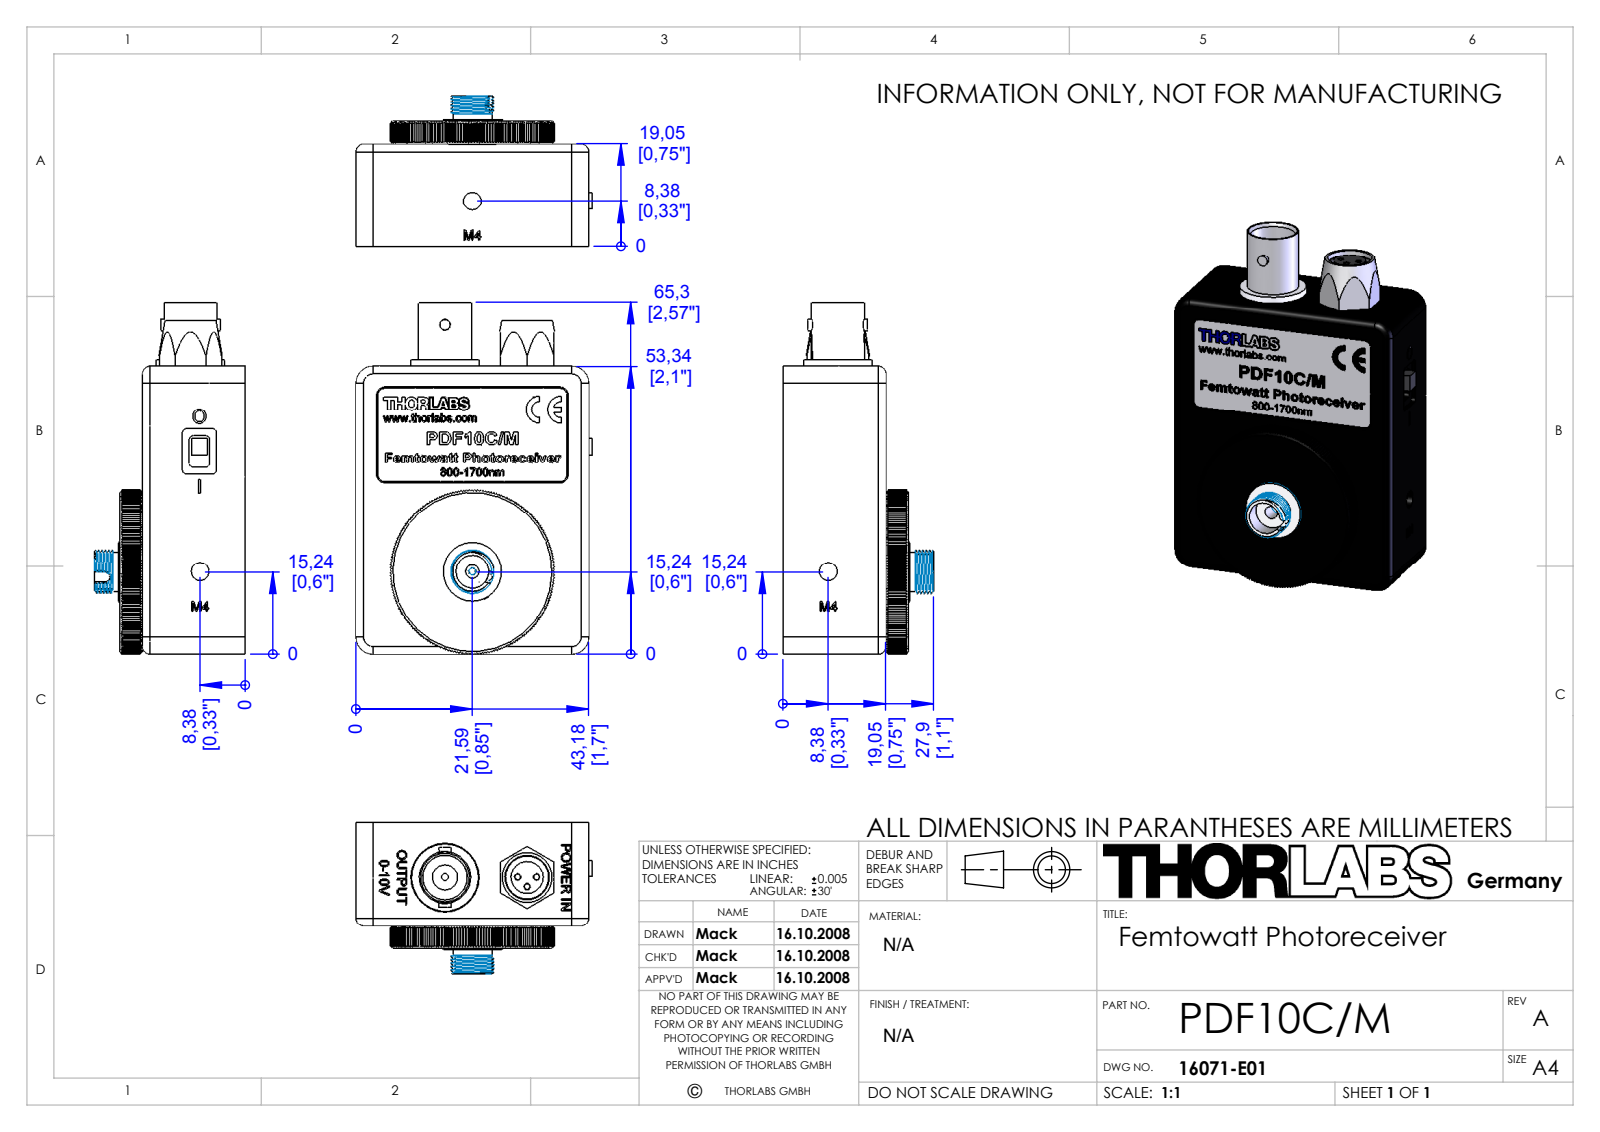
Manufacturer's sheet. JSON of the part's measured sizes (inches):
{"part_name": "BNCBuchse-01; S120-FC_Standard; RKMF-01-3polig; 16071-E01 (+6 more)", "step_written_by": "SolidWorks 2008 (CONFIG_CONTROL_DESIGN)", "units": "inches", "bodies": {"solids": 8, "faces": 2682, "planar": 1723, "cylindrical": 440, "other": 519}, "overall_size": [2.571, 1.726, 1.1], "volume_in3": 1.283, "surface_area_in2": 40.71, "round_holes": [[0.063, 7], [0.039, 5], [0.094, 4], [0.028, 3], [0.096, 3], [0.05, 2], [0.13, 2], [0.052, 1], [0.098, 1], [0.118, 1], [0.15, 1], [0.165, 1]], "round_bosses_or_shafts": [[0.02, 6], [0.018, 2], [1.035, 1], [0.531, 1], [0.49, 1], [0.43, 1], [0.425, 1], [0.378, 1]], "partial_cylinders_radius": [[0.125, 32], [0.13, 12], [0.031, 10], [0.031, 8], [0.095, 8], [0.05, 4], [0.055, 4], [0.063, 3]], "face_to_face_distances": [0.063, 0.1, 0.031, 0.421, 0.483, 0.05, 0.452, 0.389, 0.246, 0.07], "hole_center_spacings": [0.069, 0.1, 0.05, 0.097, 0.107, 0.116, 0.141, 0.72]}
